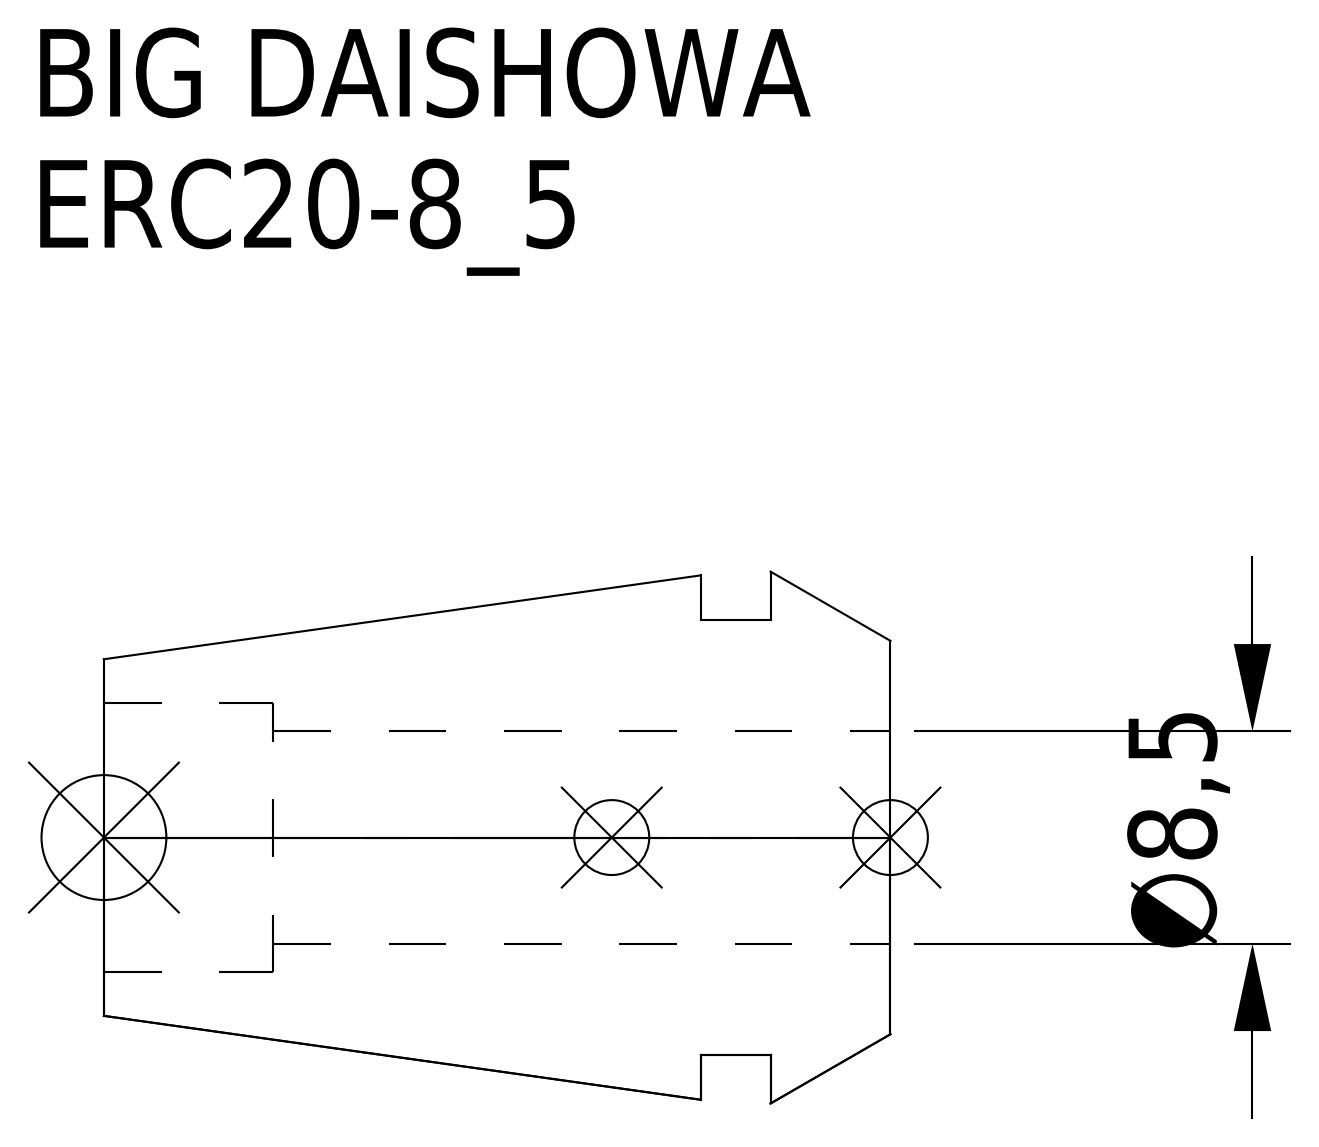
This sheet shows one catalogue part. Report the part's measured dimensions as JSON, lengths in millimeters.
{"part_name": "ERC20-8_5", "step_written_by": "CREO PARAMETRIC BY PTC INC, 2016380 (AUTOMOTIVE_DESIGN)", "units": "millimeters", "bodies": {"solids": 1, "faces": 15, "planar": 5, "cylindrical": 6, "other": 4}, "overall_size": [31.5, 21.3, 21.3], "volume_mm3": 5859, "surface_area_mm2": 3172, "round_holes": [[8.5, 1], [10.8, 1]], "round_bosses_or_shafts": [[17.4, 1]], "face_to_face_distances": [4.8, 7.6, 2.8, 31.5, 26.7, 23.9, 24.72, 19.92, 17.12, 6.78]}
